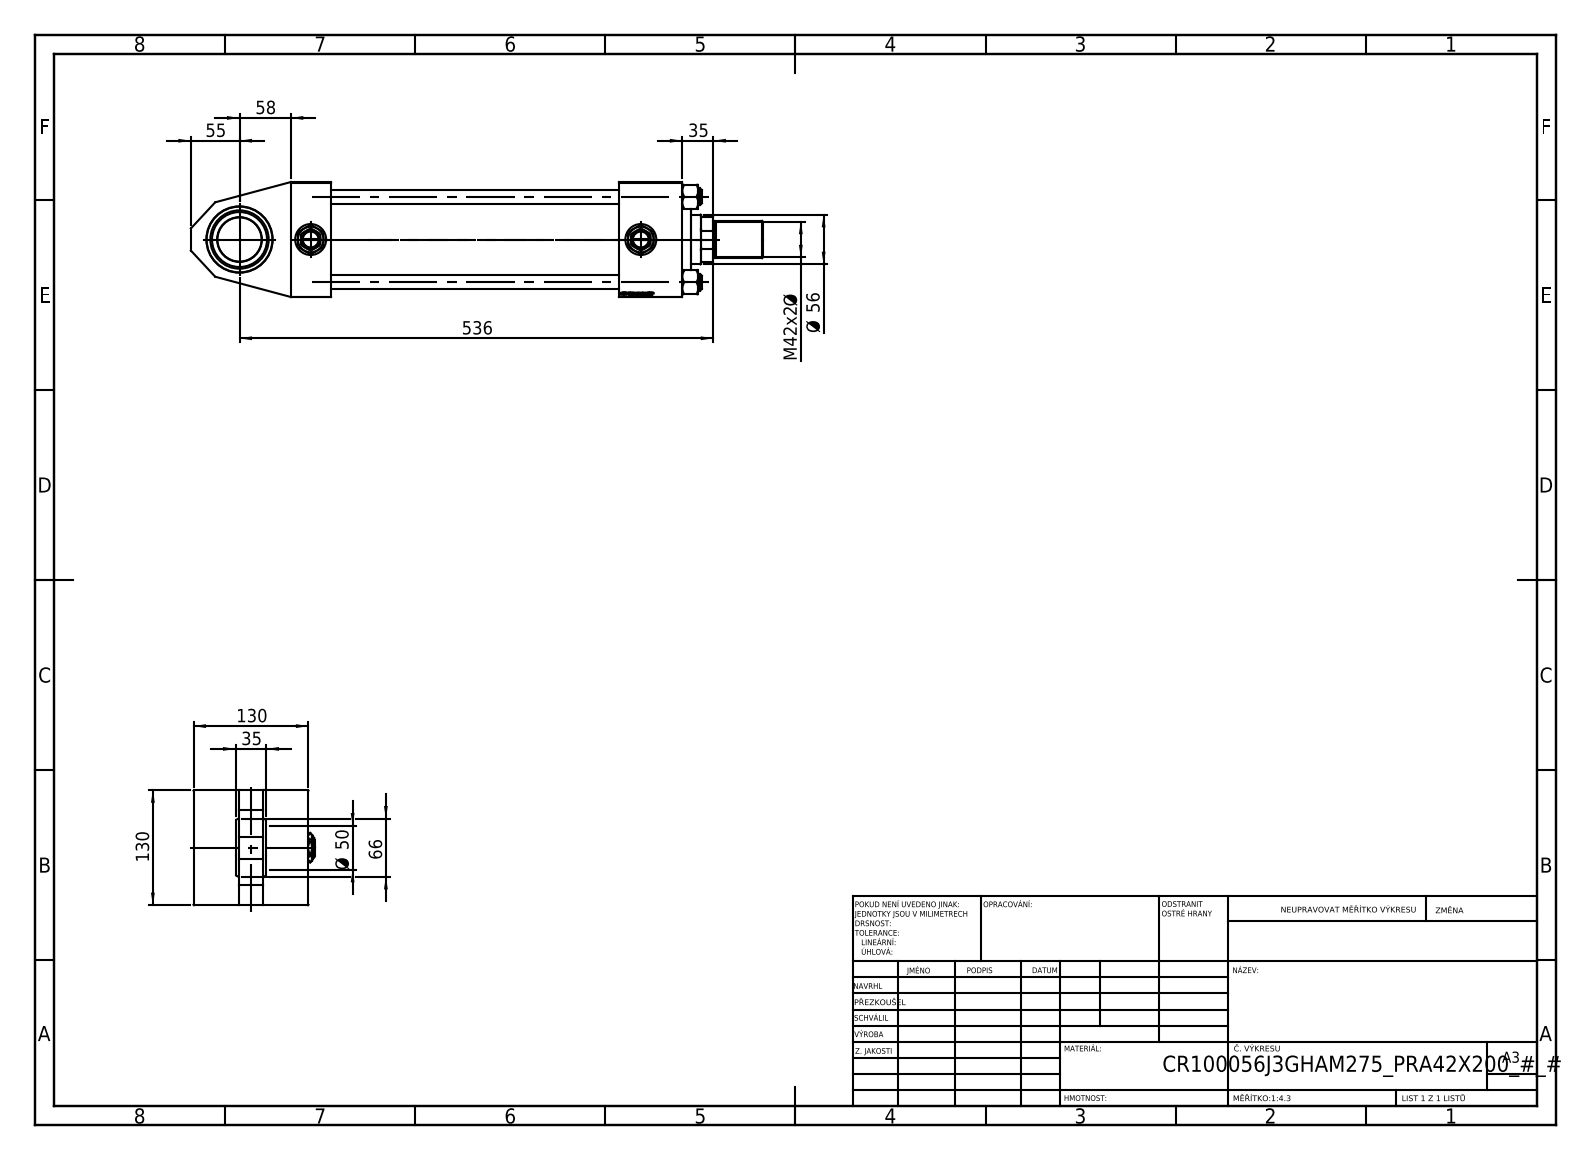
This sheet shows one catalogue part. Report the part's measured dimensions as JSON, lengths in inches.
{"part_name": "V215CR_J_Body; Zatka_pro_OIL_PORT; V215CR_VCP_J; ROD_END_AH (+4 more)", "step_written_by": "SolidWorks 2019 (CONFIG_CONTROL_DESIGN)", "units": "inches", "bodies": {"solids": 15, "faces": 1308, "planar": 616, "cylindrical": 104, "other": 588}, "overall_size": [25.472, 5.394, 5.118], "volume_in3": 237.7, "surface_area_in2": 1020, "round_holes": [[0.63, 4], [0.098, 2], [0.276, 2], [1.041, 2], [1.378, 2], [1.594, 1], [1.969, 1], [2.205, 1], [2.323, 1], [2.953, 1], [2.992, 1], [3.366, 1]], "round_bosses_or_shafts": [[0.748, 4], [4.173, 1], [2.835, 1], [1.654, 1], [1.575, 1]], "partial_cylinders_radius": [[1.063, 1]], "face_to_face_distances": [5.118, 2.008, 3.11, 1.772, 17.441, 15.669, 14.606, 12.835, 2.835, 1.102], "hole_center_spacings": [1.93, 2.698, 3.815, 4.005, 1.614, 5.395, 3.169, 3.228]}
